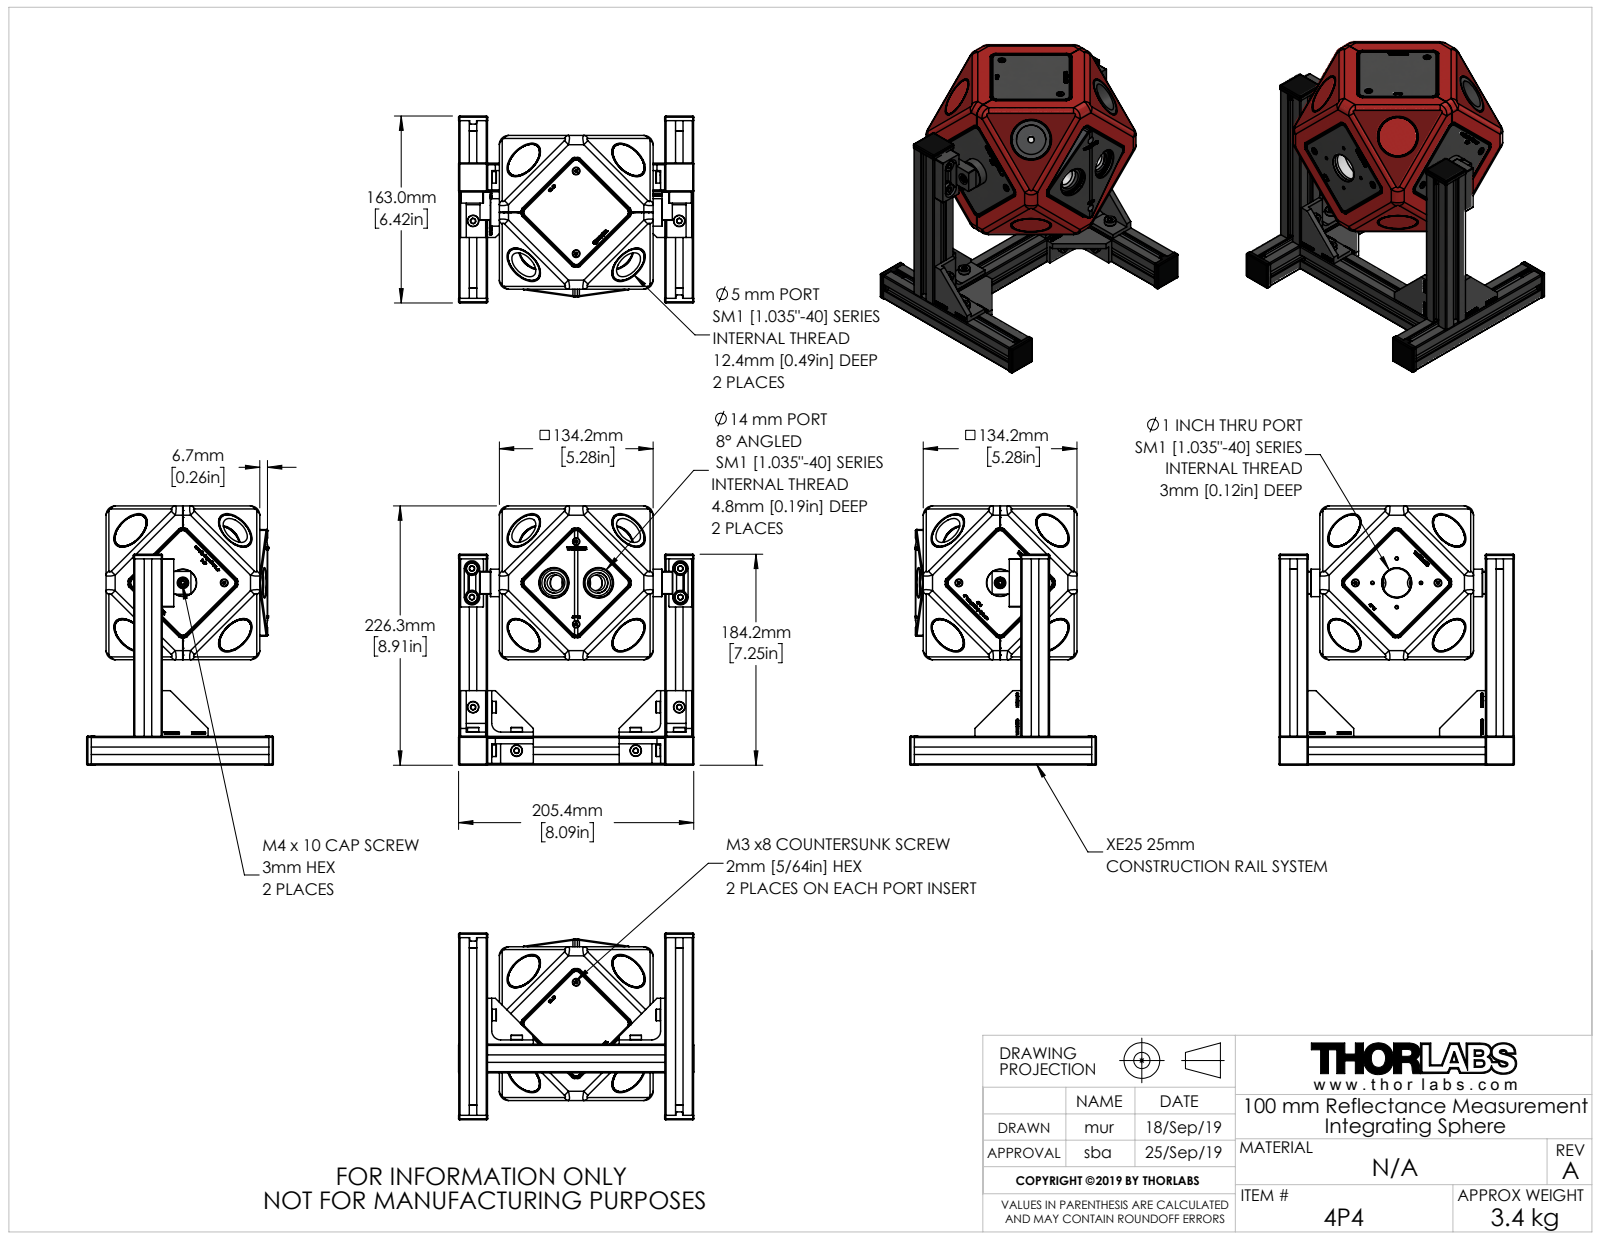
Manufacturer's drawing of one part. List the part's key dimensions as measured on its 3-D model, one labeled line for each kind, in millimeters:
Part name (STEP PRODUCT): 19.11.08_4P4_Four Inch IS PM Config WEB
STEP written by: SolidWorks 2018 (AUTOMOTIVE_DESIGN)
Units: millimetres
Bodies: 0 solids, 10565 faces (6130 planar, 1845 cylindrical, 2590 other)
Overall size (bounding box): 226.3 × 205.39 × 163
Round holes (diameter × count): ⌀4.04 ×20, ⌀5 ×19, ⌀5.5 ×15, ⌀4 ×12, ⌀4.5 ×12, ⌀6.5 ×12, ⌀2.5 ×8, ⌀3.2 ×8, ⌀30.5 ×8, ⌀32.3 ×8, ⌀34.8 ×8, ⌀2.26 ×4
Round bosses / shafts (diameter × count): ⌀10 ×14, ⌀6 ×14, ⌀34 ×8, ⌀32 ×8, ⌀5.7 ×8, ⌀3 ×8, ⌀34.1 ×6, ⌀5.5 ×6
Partial cylindrical surfaces — rounded edges, fillets, slot ends (radius × count): R0.2 ×300, R1 ×232, R0.5 ×68, R0.25 ×64, R2 ×56, R6 ×36, R0.8 ×32, R2.5 ×24
Main face-to-face distances: 3, 128, 3.1, 131.1, 131, 17.9, 134.1, 118.2, 8, 25
Hole centre spacings: 30.7, 12.02, 17, 25.74, 47.27, 53.91, 38, 12.01
